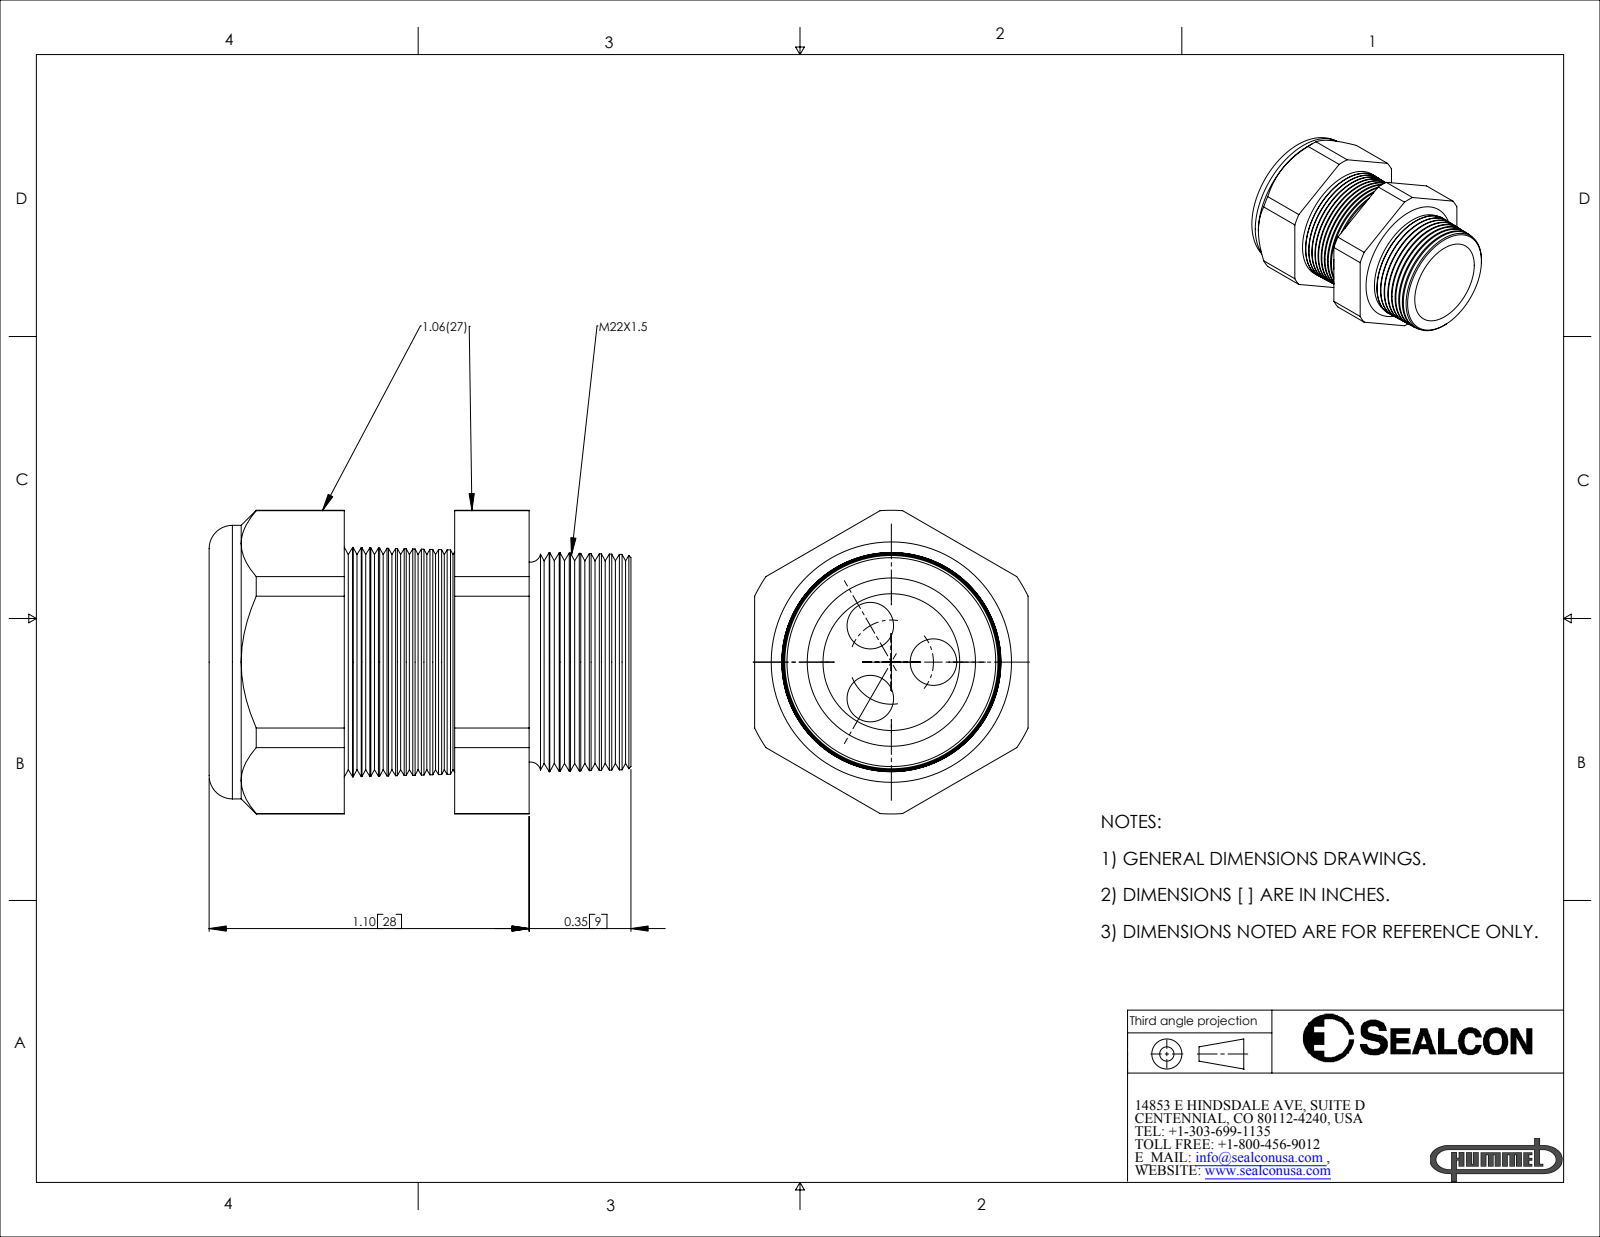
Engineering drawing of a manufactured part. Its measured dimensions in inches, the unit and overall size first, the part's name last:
Units: inches
Overall size (bounding box): 1.45 × 1.043 × 0.94
Round holes (diameter × count): ⌀0.16 ×3, ⌀0.45 ×1, ⌀0.47 ×1
Round bosses / shafts (diameter × count): ⌀0.94 ×1
Partial cylindrical surfaces — rounded edges, fillets, slot ends (radius × count): R0.522 ×1
Main face-to-face distances: 0.94, 0.844, 0.465, 0.38, 1.1, 0.635, 0.256, 1.45, 0.985, 0.606
Hole centre spacings: 0.144, 0.25
Volume: 0.581 in³ · Surface area: 10.25 in²
Bodies: 2 solids, 192 faces (20 planar, 26 cylindrical, 146 other)
Part name (STEP PRODUCT): CD22M2-BK
STEP written by: SolidWorks 2007 (CONFIG_CONTROL_DESIGN)
